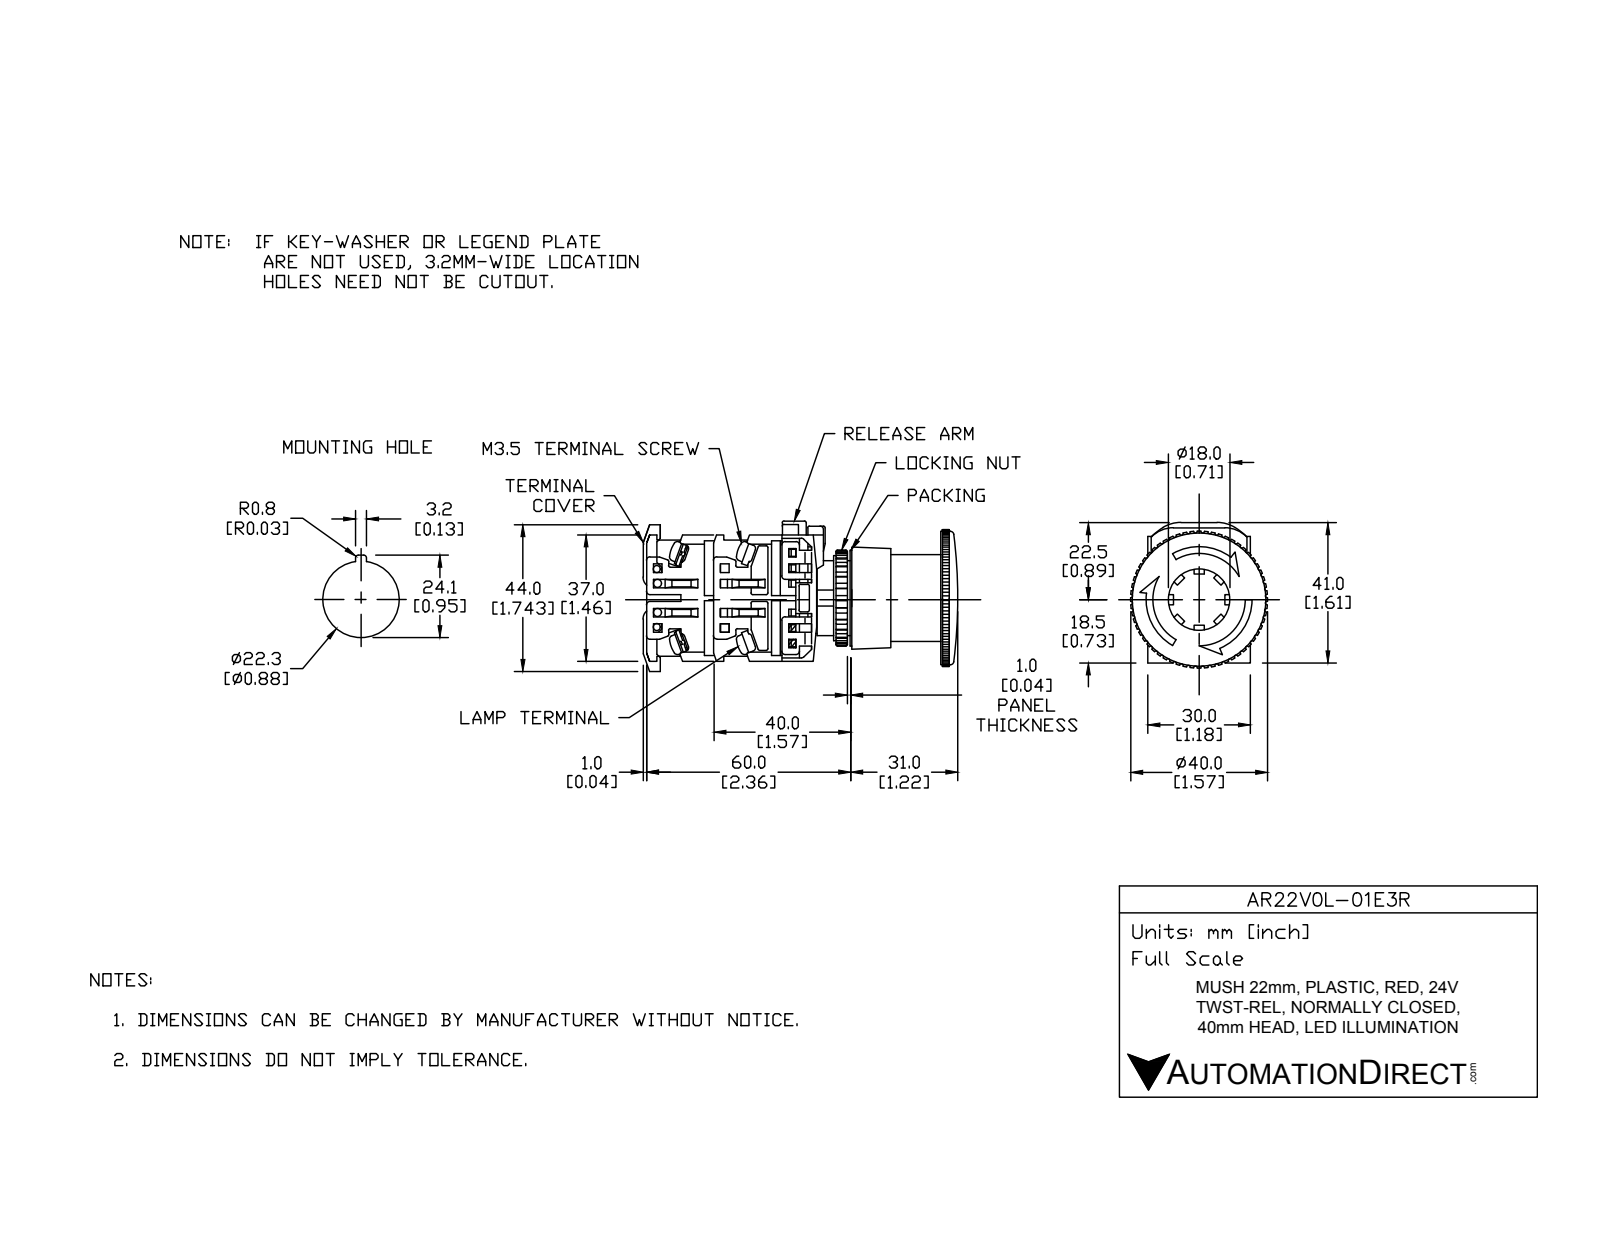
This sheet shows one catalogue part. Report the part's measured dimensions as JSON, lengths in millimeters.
{"part_name": "AR22V0L-01E3R", "step_written_by": "SolidWorks 2017 (AUTOMOTIVE_DESIGN)", "units": "millimeters", "bodies": {"solids": 17, "faces": 725, "planar": 308, "cylindrical": 310, "other": 107}, "overall_size": [72.5, 43.81, 39.99], "volume_mm3": 45768, "surface_area_mm2": 26387, "round_holes": [[21.8, 1], [22, 1], [25.4, 1]], "round_bosses_or_shafts": [[5, 4], [29.8, 1], [25, 1], [24, 1], [21.75, 1], [17, 1]], "partial_cylinders_radius": [[0.5, 119], [1.75, 8], [5, 4], [4, 2], [13.5, 1], [15, 1], [16.59, 1], [17.59, 1]], "face_to_face_distances": [1, 29, 10, 18, 2, 20, 16, 22.5, 20.5, 26]}
